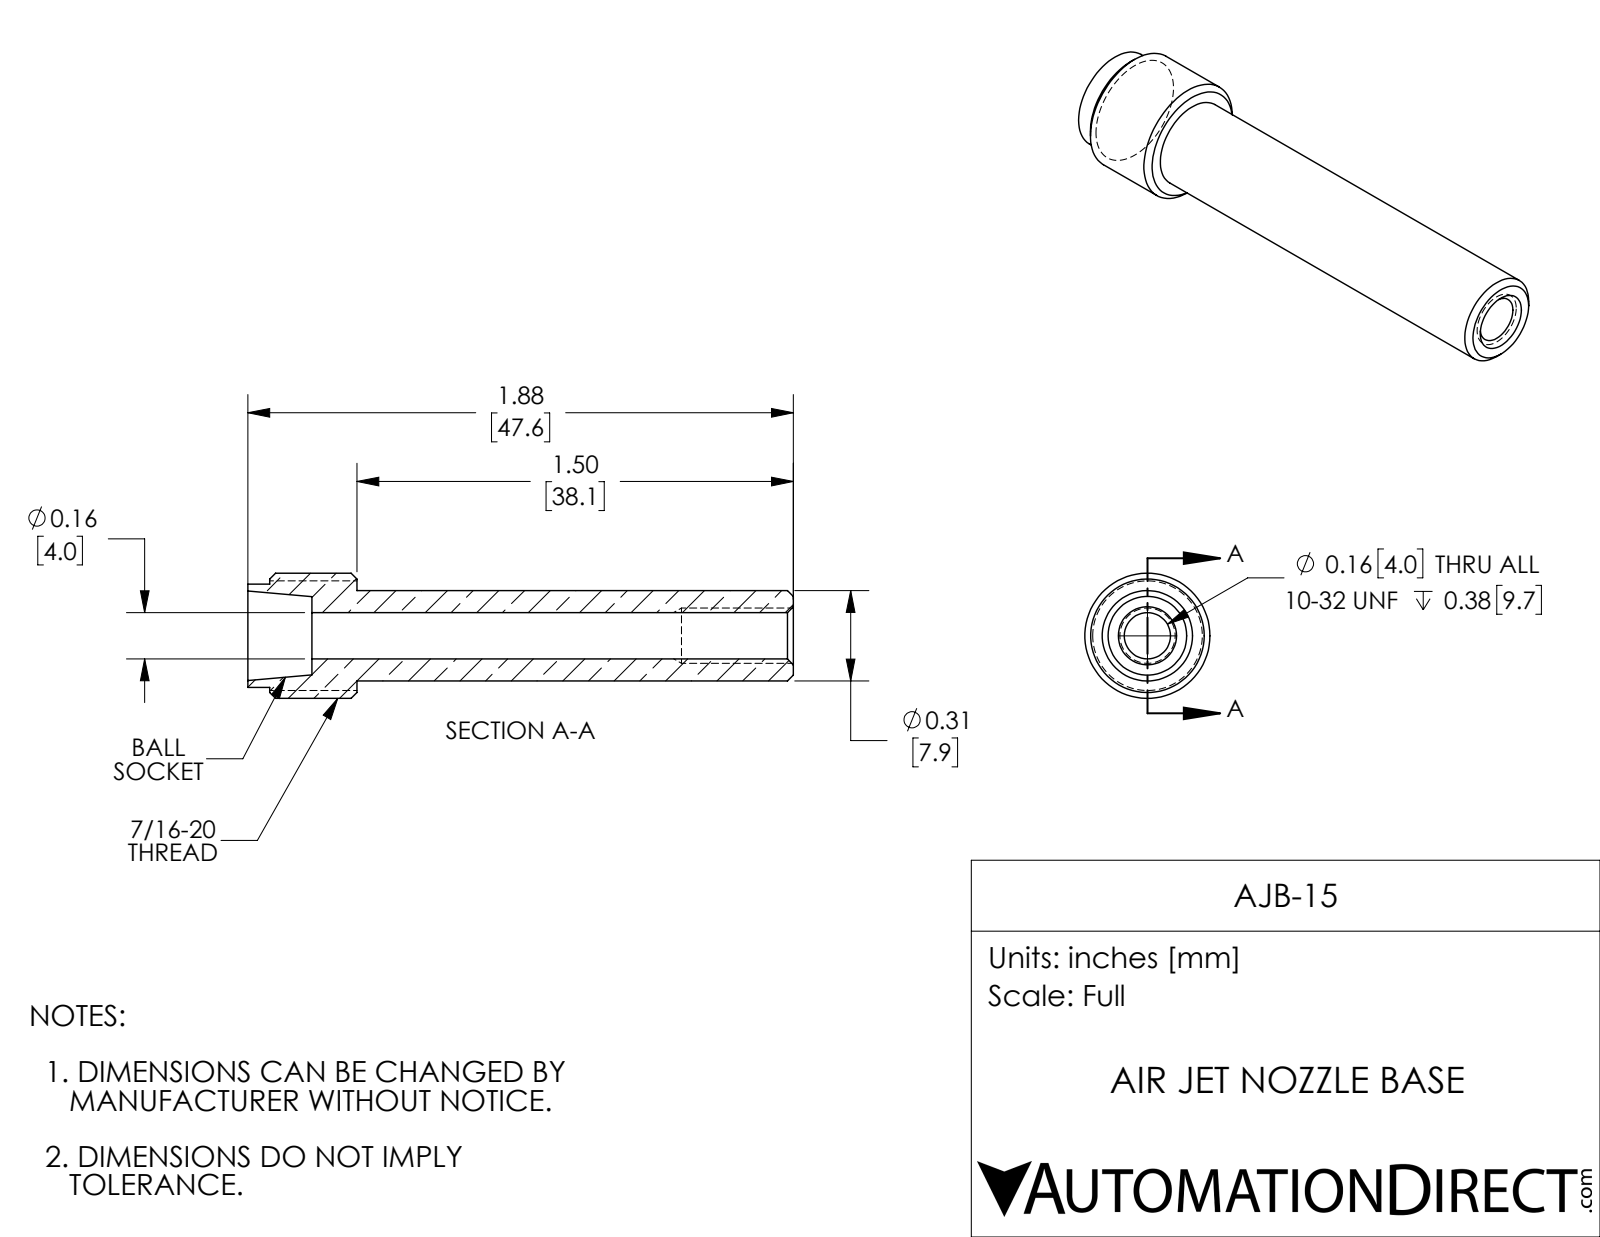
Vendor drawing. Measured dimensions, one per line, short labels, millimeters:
name: AJB-15
written by: SolidWorks 2018 (AUTOMOTIVE_DESIGN)
unit: mm
bodies: 1 solid, 23 faces (5 planar, 8 cylindrical, 10 other)
size: 47.6 × 10.9 × 10.9
volume: 1 920 mm³; area: 2 040 mm²
holes: 1× ⌀4
bosses: 1× ⌀10.9, 1× ⌀9, 1× ⌀7.9
face distances: 3.9, 38.1, 42, 47.6, 9.5, 5.6, 45.7, 7.6, 3.7, 1.9
